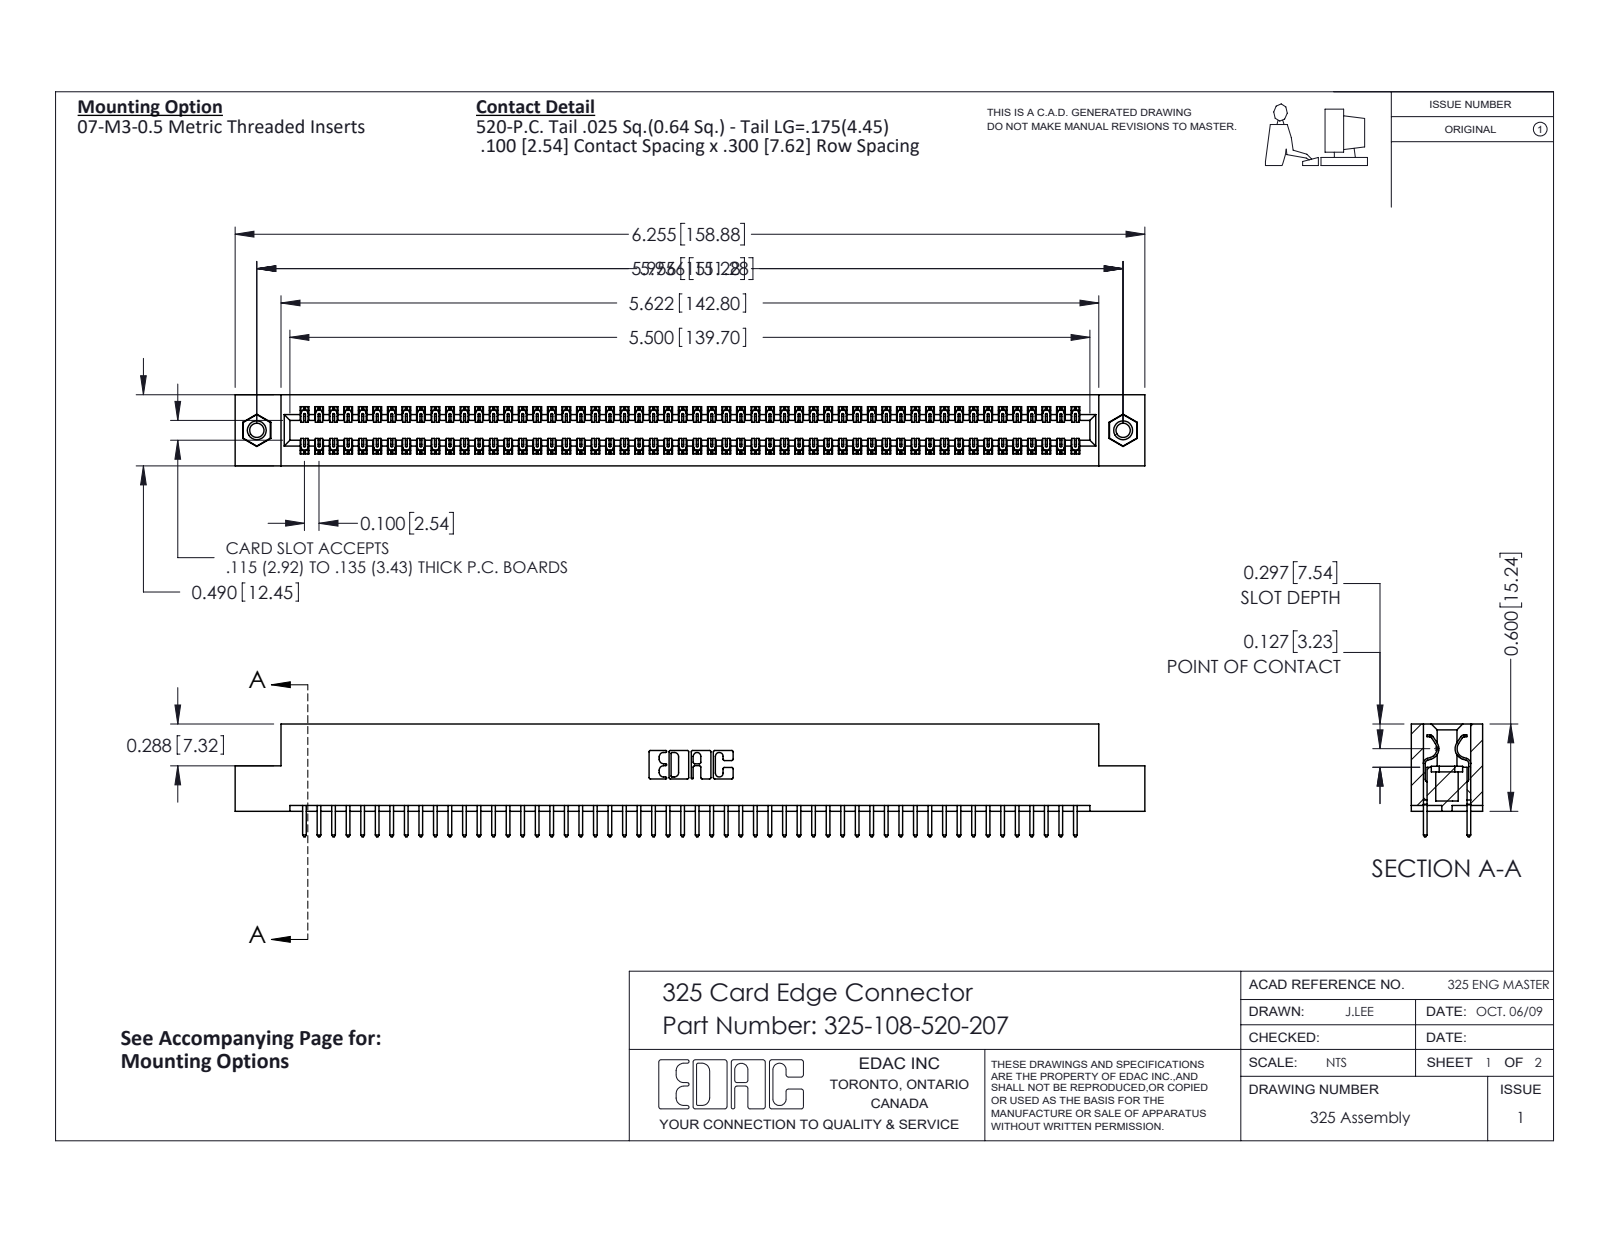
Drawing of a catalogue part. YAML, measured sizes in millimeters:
part_name: "325-292-001_325-293-120; 325 Part_TI; 325-108-520-207; 345-250-001_345-250-005-103"
step_written_by: "SolidWorks 2016 (CONFIG_CONTROL_DESIGN)"
units: millimeters
bodies: {solids: 111, faces: 5790, planar: 3990, cylindrical: 1784, other: 16}
overall_size: [158.9, 19.7, 12.4]
volume: 20580
surface_area: 25010
round_holes:
  - {diameter: 2.5, count: 2}
  - {diameter: 3.2, count: 2}
  - {diameter: 4.1, count: 2}
round_bosses_or_shafts:
  - {diameter: 3.9, count: 2}
partial_cylinders:
  - {radius: 0.2, count: 162}
  - {radius: 0.3, count: 108}
  - {radius: 0.3, count: 22}
  - {radius: 0.2, count: 6}
  - {radius: 0.8, count: 6}
  - {radius: 0.7, count: 3}
  - {radius: 0.4, count: 2}
  - {radius: 0.6, count: 2}
face_to_face_distances: [2.1, 10.3, 7.6, 12.4, 2.7, 9.7, 0.6, 8.3, 7, 14.2]
hole_center_spacings: [151.3]
